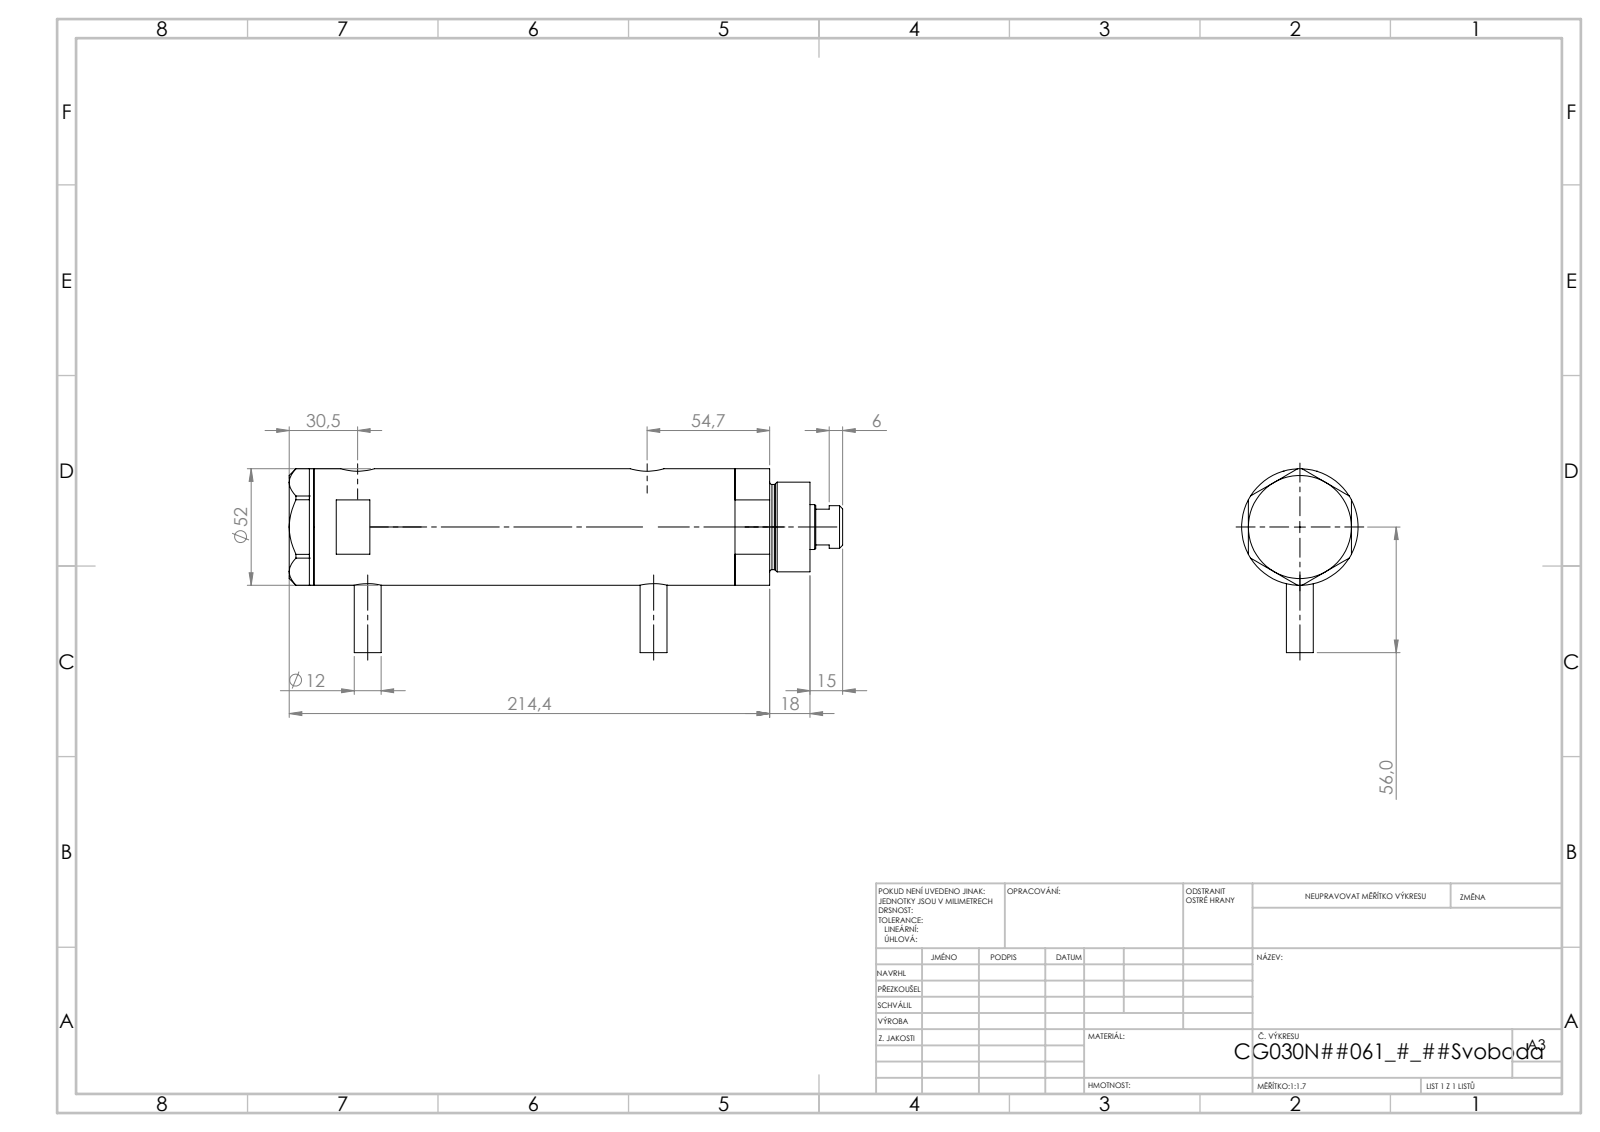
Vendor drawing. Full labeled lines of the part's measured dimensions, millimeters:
Part name (STEP PRODUCT): V270CG_FRONT; V270CG_VC; V270CG_BACK; V270CG_MIDDLE
STEP written by: SolidWorks 2019 (CONFIG_CONTROL_DESIGN)
Units: millimetres
Bodies: 4 solids, 140 faces (67 planar, 53 cylindrical, 20 other)
Overall size (bounding box): 246.97 × 82 × 52
Volume: 454 562 mm³ · Surface area: 100 240 mm²
Round holes (diameter × count): ⌀5 ×2, ⌀9.73 ×2, ⌀12.5 ×2, ⌀15 ×2, ⌀6.5 ×1, ⌀20 ×1, ⌀21.5 ×1, ⌀30 ×1, ⌀33 ×1, ⌀44 ×1
Round bosses / shafts (diameter × count): ⌀12 ×2, ⌀52 ×1, ⌀40 ×1, ⌀38 ×1, ⌀19 ×1
Main face-to-face distances: 151.5, 23.8, 127.7, 11, 34.8, 162.5, 46, 198.9, 187.9, 164.1
Hole centre spacings: 2.9, 4.5, 124.7, 127.6, 129.2, 132.1
